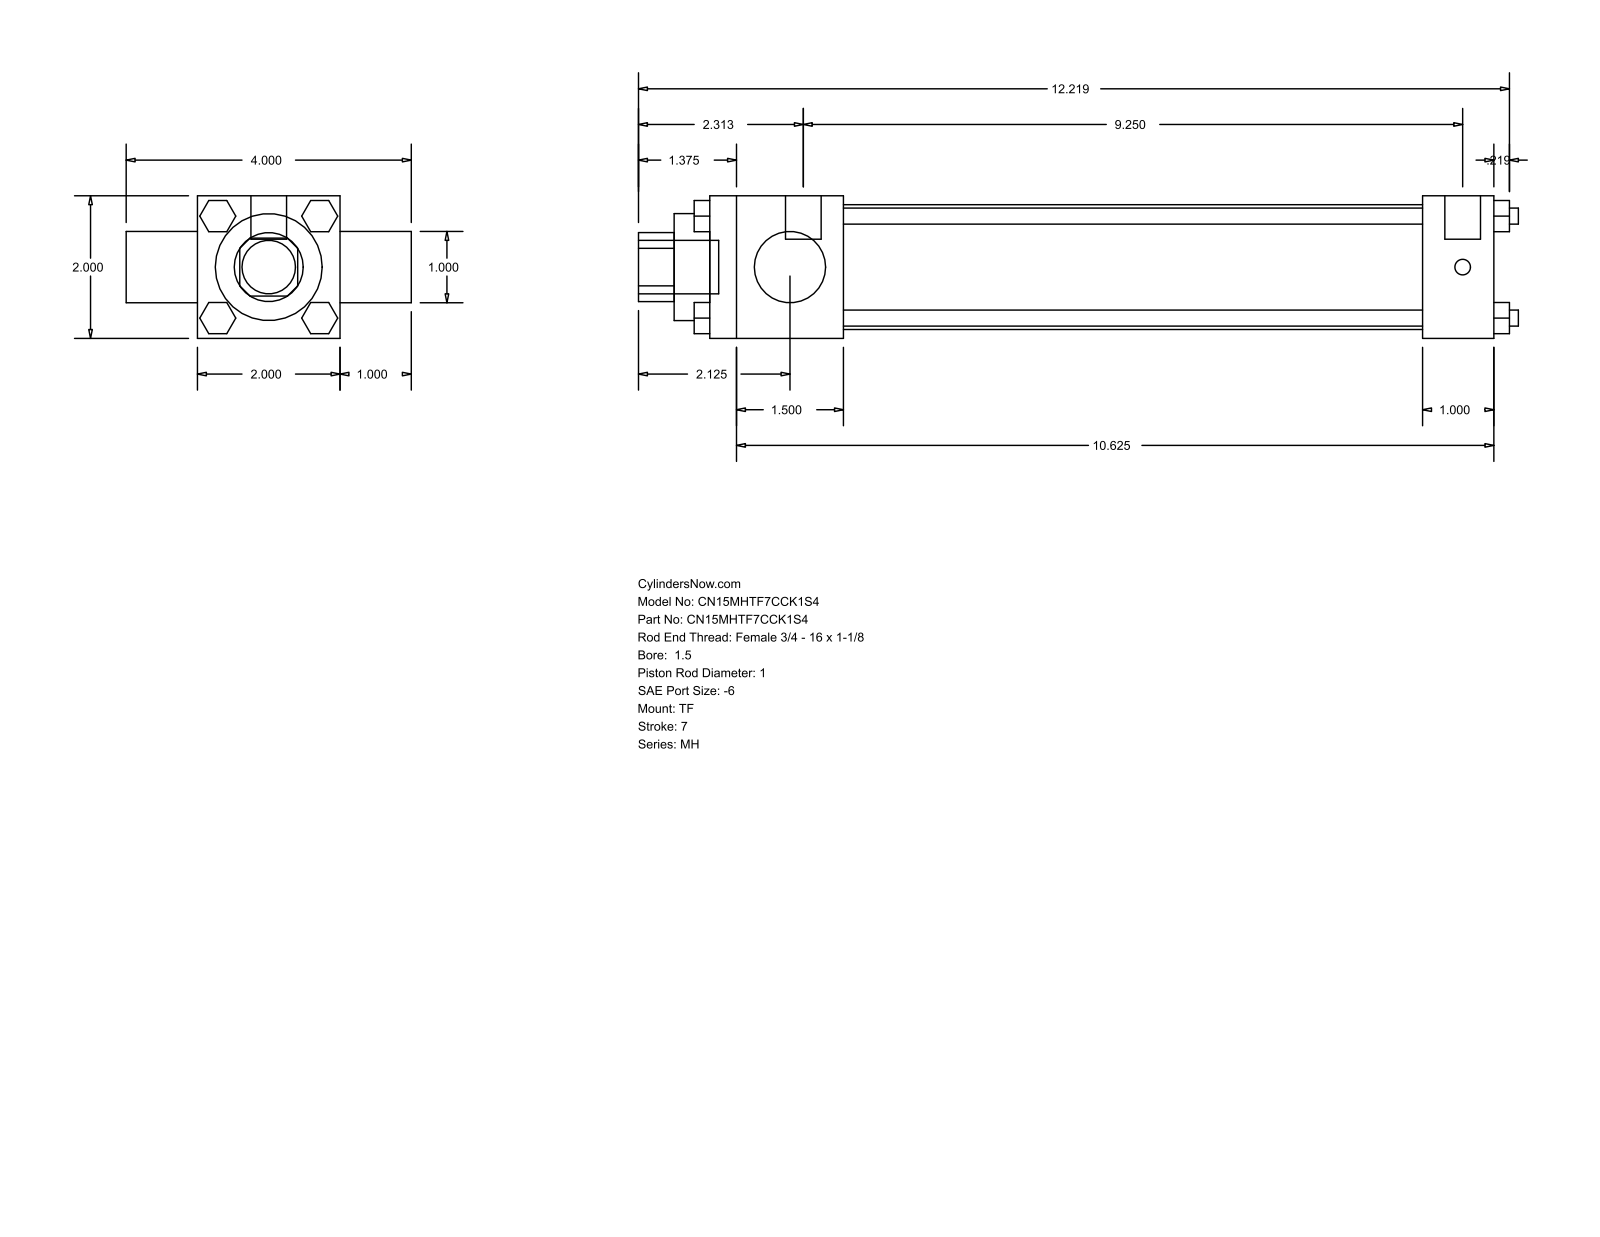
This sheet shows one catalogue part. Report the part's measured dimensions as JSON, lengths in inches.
{"part_name": "MH_TF__0150_1", "step_written_by": "GSSL Pune (CONFIG_CONTROL_DESIGN)", "units": "inches", "bodies": {"solids": 0, "faces": 120, "planar": 92, "cylindrical": 28, "other": 0}, "overall_size": [12.344, 4, 2], "round_holes": [[1, 2], [1.5, 1], [1.75, 1]], "round_bosses_or_shafts": [[0.225, 4], [0.219, 3], [0.5, 2], [0.75, 1]], "partial_cylinders_radius": [[0.484, 1]], "face_to_face_distances": [2, 1, 11, 3, 1.875, 9.125, 10, 8.125, 11.219, 0.5]}
